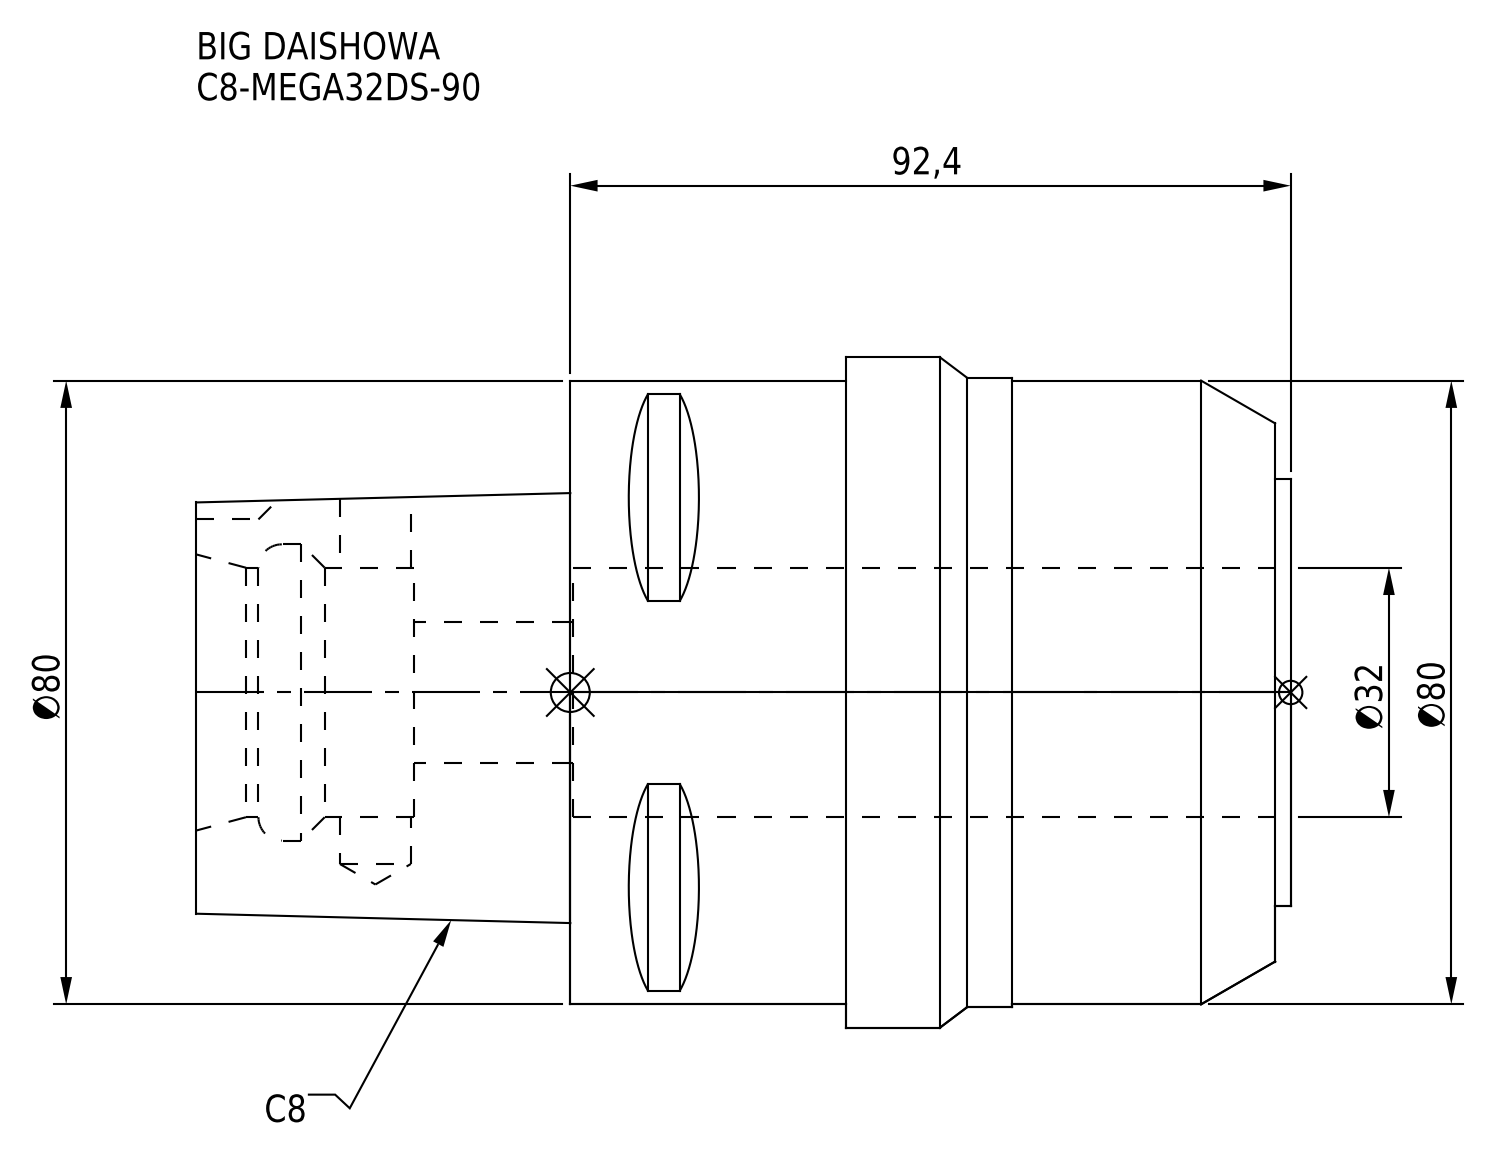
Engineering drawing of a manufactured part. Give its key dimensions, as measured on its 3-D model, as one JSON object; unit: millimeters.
{"part_name": "C8-MEGA32DS-90", "step_written_by": "CREO PARAMETRIC BY PTC INC, 2016380 (AUTOMOTIVE_DESIGN)", "units": "millimeters", "bodies": {"solids": 1, "faces": 69, "planar": 30, "cylindrical": 25, "other": 14}, "overall_size": [140.4, 86, 86], "volume_mm3": 464329, "surface_area_mm2": 55206, "round_holes": [[9.1, 1], [18, 1], [32, 1], [38, 1]], "round_bosses_or_shafts": [[86, 1], [80.7, 1], [80, 1], [54.7, 1]], "partial_cylinders_radius": [[6, 1]], "face_to_face_distances": [92.4, 2, 90.4, 140.4, 138.4, 48, 57, 55, 35.4, 83.4]}
